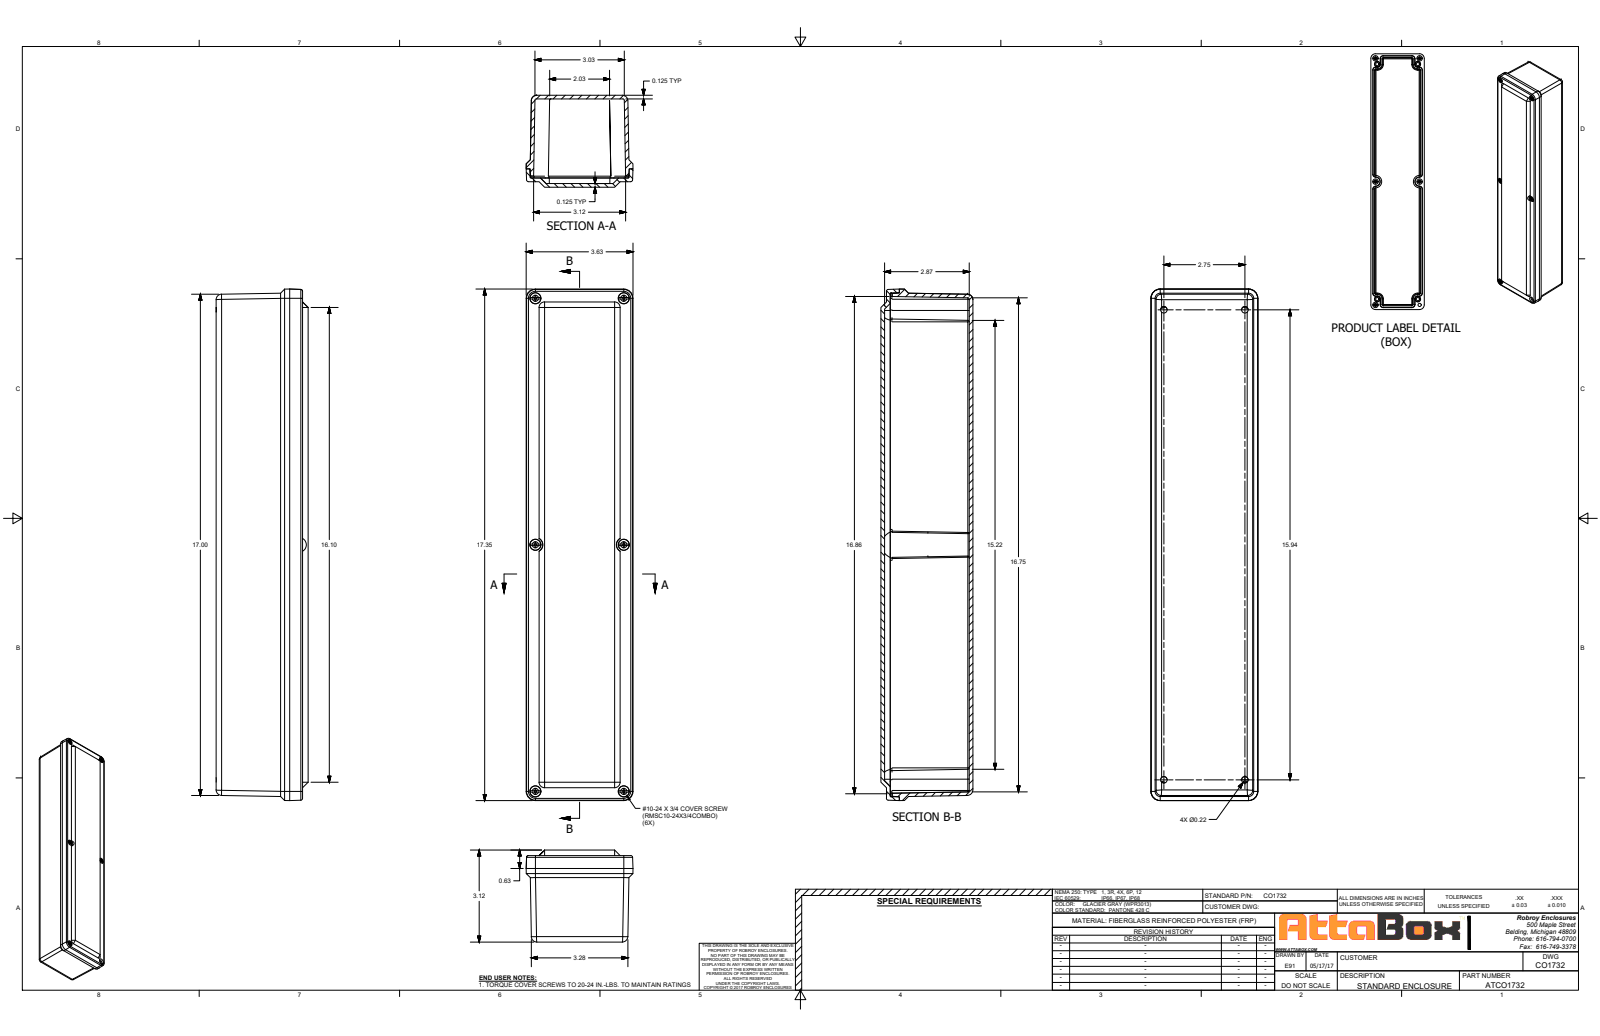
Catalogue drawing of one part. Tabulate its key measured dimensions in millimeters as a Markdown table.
| quantity | value |
| --- | --- |
| part name | CO1732 |
| STEP written by | SolidWorks 2018 (AUTOMOTIVE_DESIGN) |
| units | millimeters |
| bodies | 15 solids, 503 faces (225 planar, 148 cylindrical, 130 other) |
| overall size | 440.6 × 92.1 × 79.2 |
| volume | 574 400 mm³ |
| surface area | 340 000 mm² |
| round holes (diameter × count) | 5.6 × 8, 4 × 6, 4.8 × 6, 9.5 × 6, 5.5 × 2 |
| round bosses / shafts (diameter × count) | 9.4 × 6, 6.9 × 6, 4.5 × 6, 11.2 × 2 |
| partial cylindrical surfaces (radius × count) | 0.3 × 24, 0.8 × 20, 1.2 × 8, 1.6 × 4, 4.5 × 4, 5.6 × 4, 7.9 × 4, 8.3 × 4 |
| main face-to-face distances | 3.2, 3.1, 76.1, 79.2, 72.9, 71.3, 4.7, 8, 1.6, 3.2 |
| hole center spacings | 10.4, 73.7, 202.4, 212.4, 215.2, 225.6, 414.8, 421.2 |
